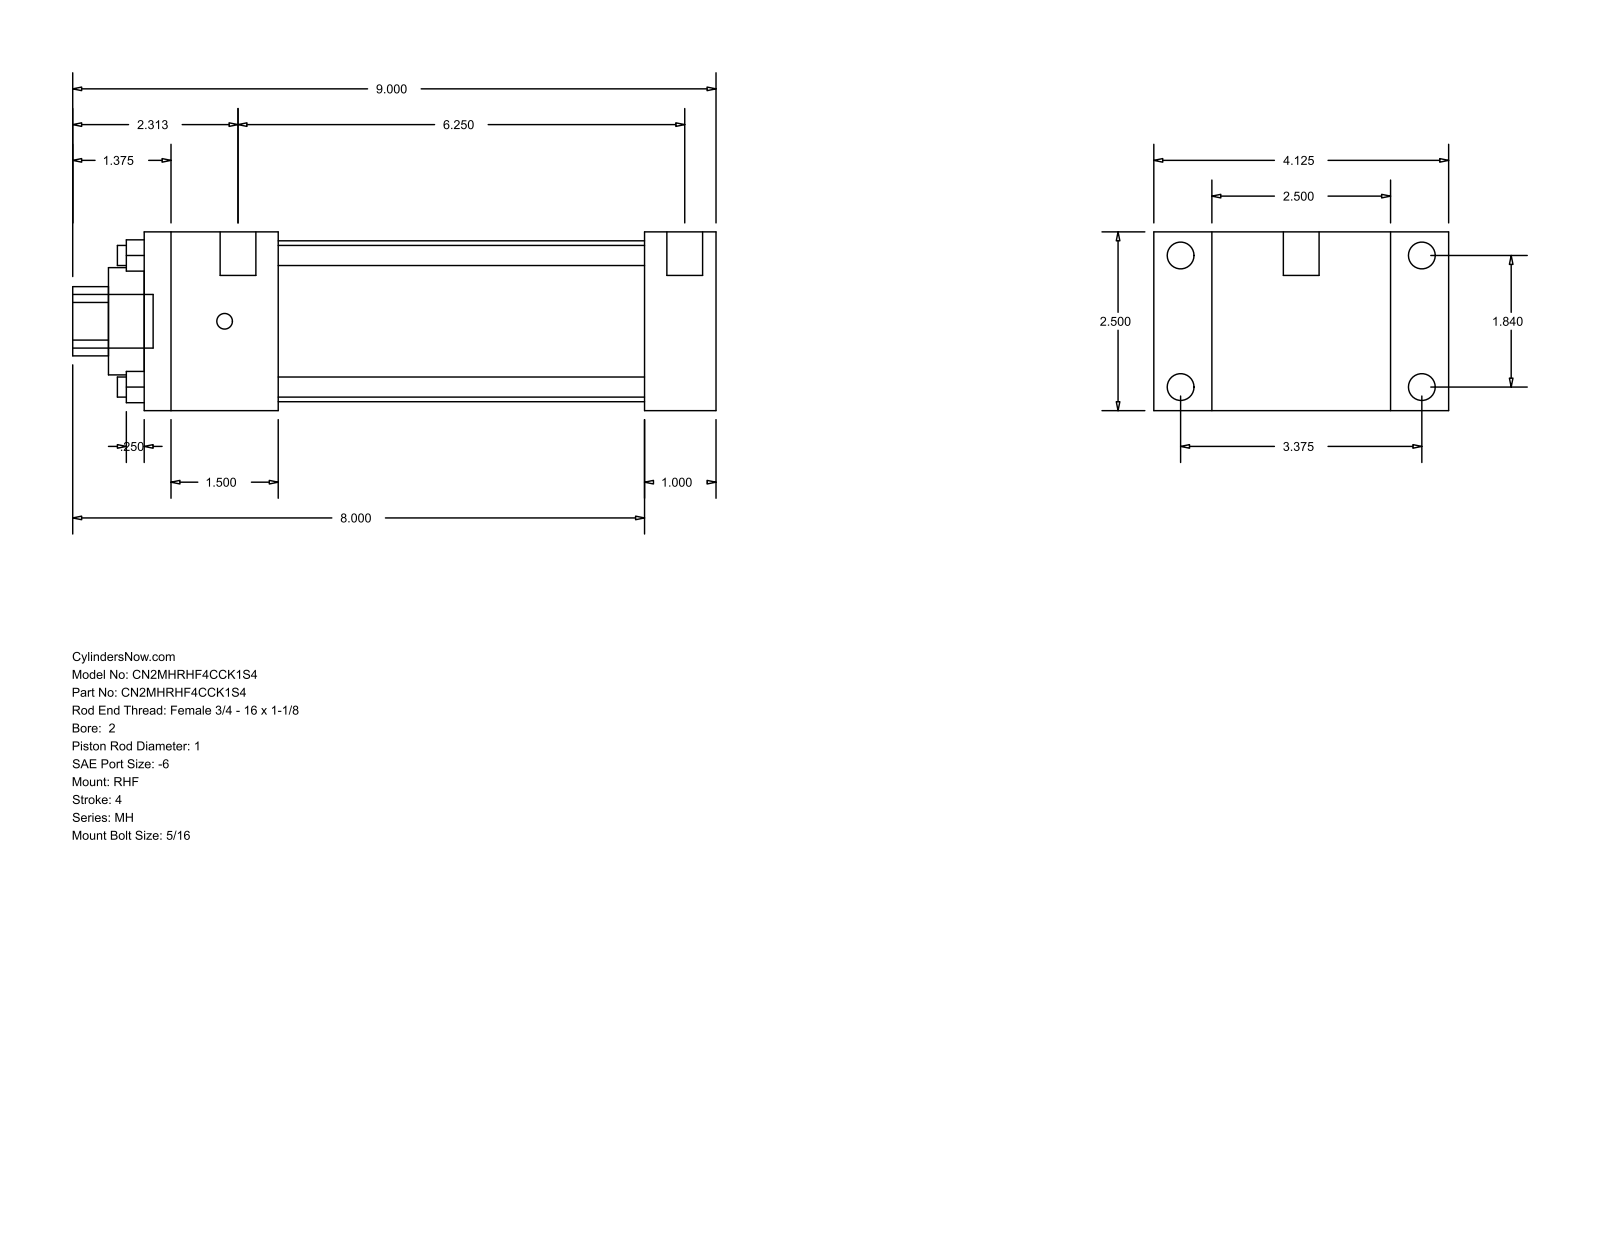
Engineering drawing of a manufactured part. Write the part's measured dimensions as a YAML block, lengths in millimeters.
part_name: "MH_RHF__0200_1"
step_written_by: "GSSL Pune (CONFIG_CONTROL_DESIGN)"
units: millimeters
bodies: {solids: 0, faces: 88, planar: 60, cylindrical: 28, other: 0}
overall_size: [228.6, 104.78, 63.5]
round_holes:
  - {diameter: 7.14, count: 4}
  - {diameter: 25.4, count: 1}
  - {diameter: 38.1, count: 1}
  - {diameter: 57.15, count: 1}
round_bosses_or_shafts:
  - {diameter: 9.53, count: 4}
  - {diameter: 5.56, count: 4}
  - {diameter: 12.7, count: 2}
  - {diameter: 19.05, count: 1}
partial_cylinders:
  - {radius: 12.29, count: 1}
face_to_face_distances: [63.5, 25.4, 20.64, 84.14, 203.2, 177.8, 104.78, 47.63, 130.17, 155.57]
hole_center_spacings: [33.05, 46.74, 66.1]
